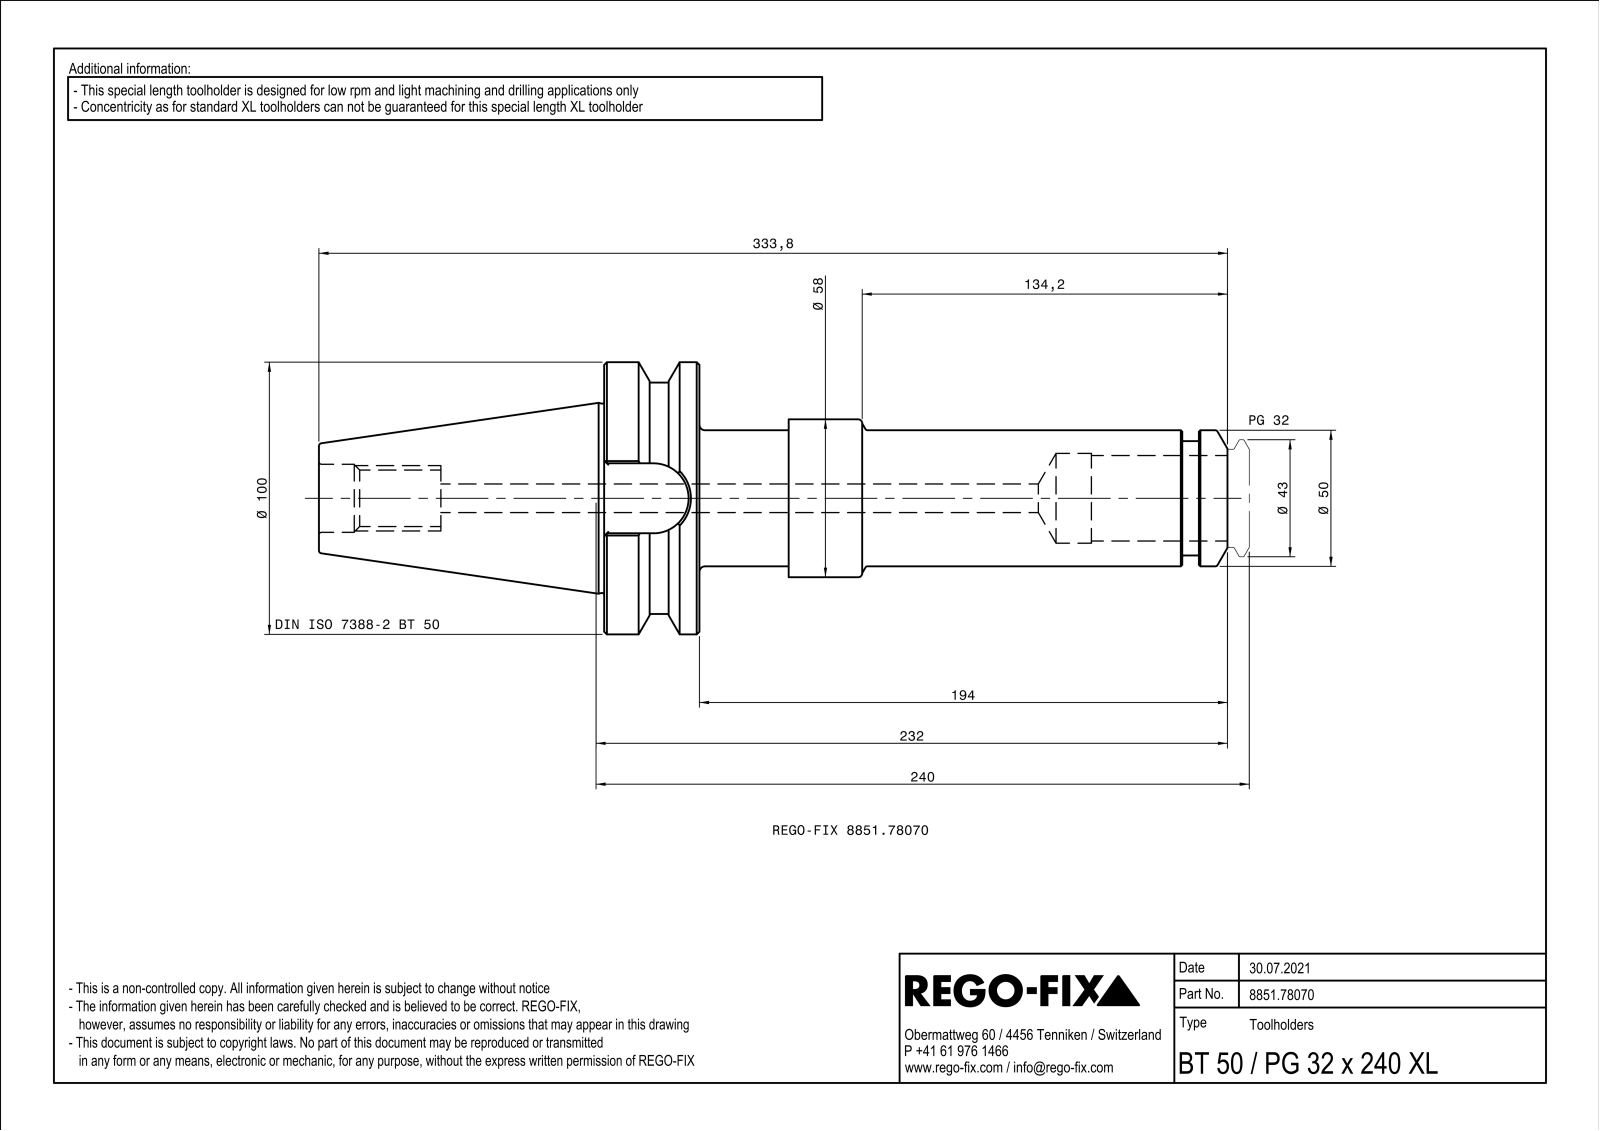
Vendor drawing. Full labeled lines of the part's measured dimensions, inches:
Part name (STEP PRODUCT): NOCUT
STEP written by: SIEMENS PLM Software Solid Edge ST10 (AUTOMOTIVE_DESIGN)
Units: inches
Bodies: 1 solid, 135 faces (41 planar, 33 cylindrical, 61 other)
Overall size (bounding box): 13.134 × 3.937 × 3.937
Volume: 46.23 in³ · Surface area: 169.8 in²
Round holes (diameter × count): ⌀0.472 ×1, ⌀0.551 ×1, ⌀0.817 ×1, ⌀0.984 ×1, ⌀1.299 ×1, ⌀2.071 ×1, ⌀2.087 ×1, ⌀2.102 ×1, ⌀2.165 ×1
Round bosses / shafts (diameter × count): ⌀3.937 ×1, ⌀3.346 ×1, ⌀2.283 ×1, ⌀1.969 ×1, ⌀1.654 ×1, ⌀1.244 ×1, ⌀1.201 ×1
Partial cylindrical surfaces — rounded edges, fillets, slot ends (radius × count): R0.02 ×4, R0.506 ×1
Main face-to-face distances: 1.378, 5.504, 2.118, 3.496, 0.24, 7.217, 6.976, 2.783, 7.622, 4.126
